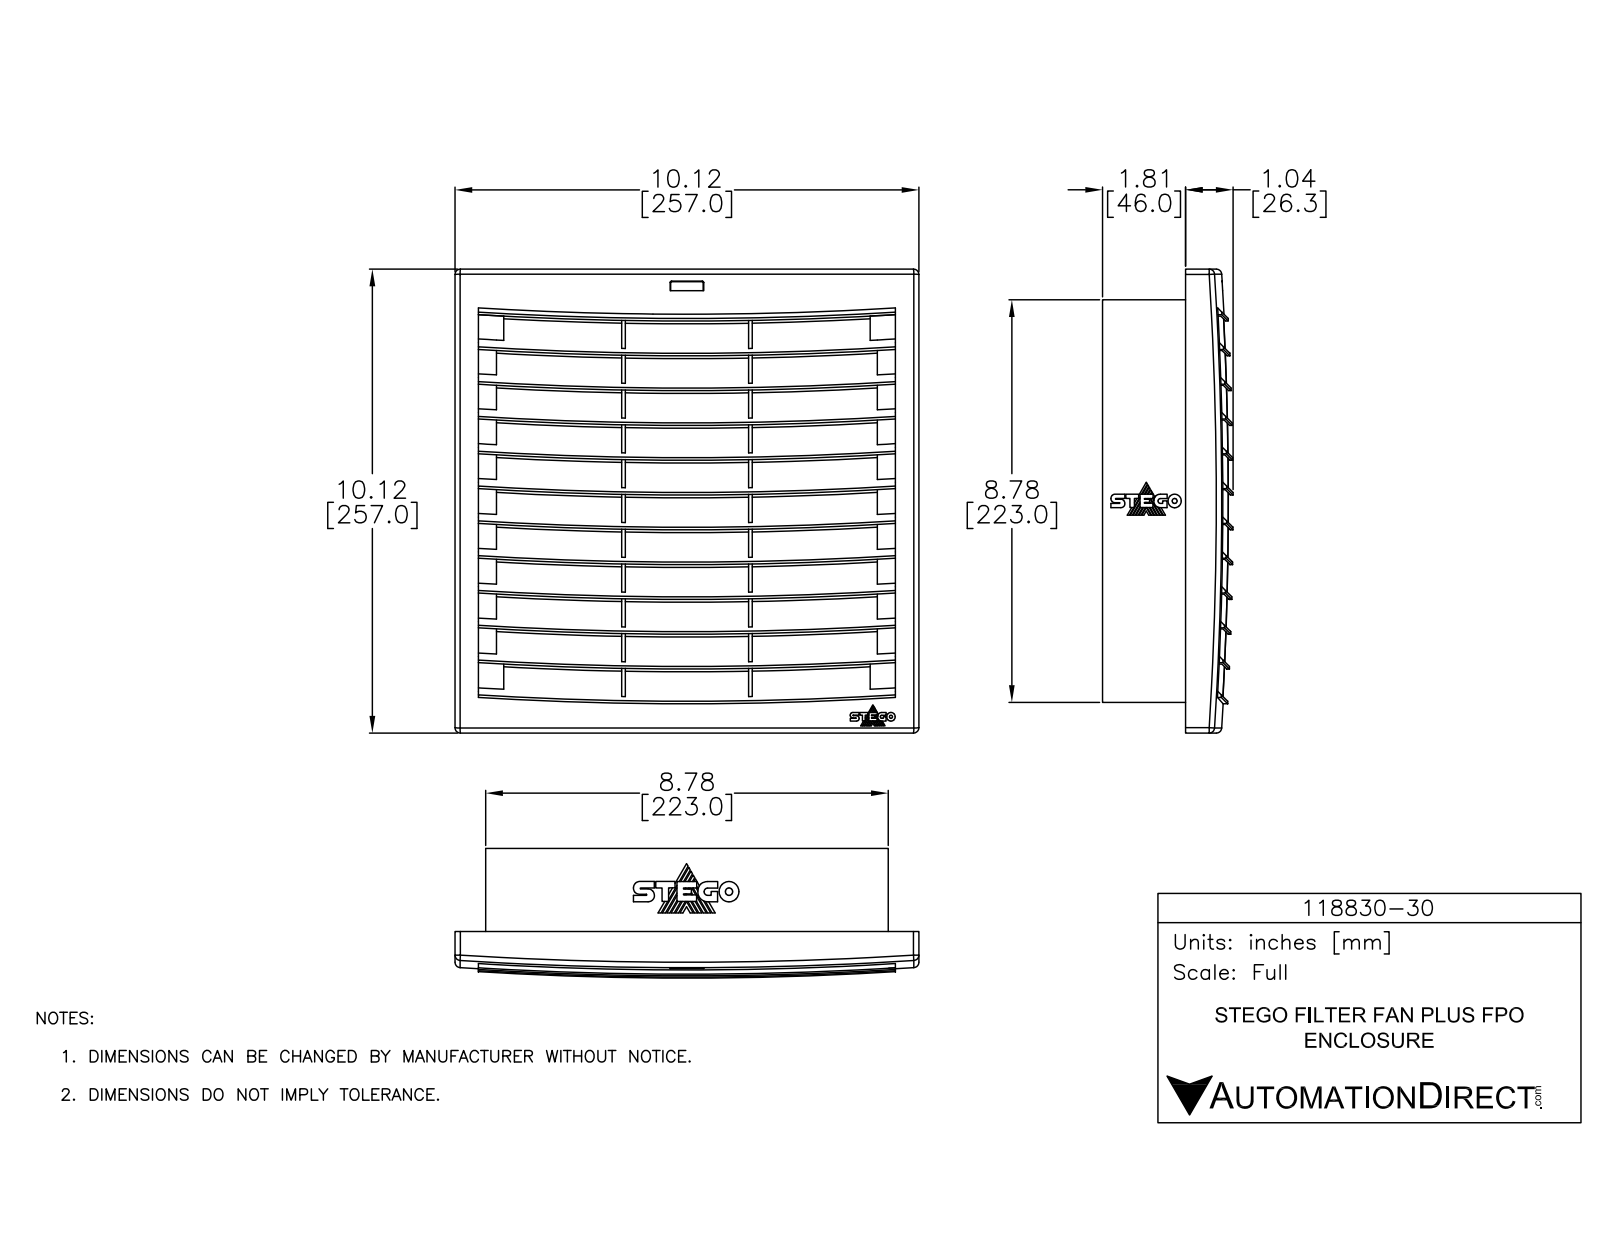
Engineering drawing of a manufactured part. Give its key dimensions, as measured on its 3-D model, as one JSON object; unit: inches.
{"part_name": "118830-30", "step_written_by": "SolidWorks 2018 (AUTOMOTIVE_DESIGN)", "units": "inches", "bodies": {"solids": 1, "faces": 180, "planar": 82, "cylindrical": 10, "other": 88}, "overall_size": [10.118, 10.118, 2.021], "volume_in3": 112.9, "surface_area_in2": 464.8, "partial_cylinders_radius": [[0.1, 4], [92.238, 1], [94.094, 1]], "face_to_face_distances": [0.079, 1.063, 0.984, 0.669, 9.449, 8.78, 10.118, 2.769, 0.553, 0.547]}
